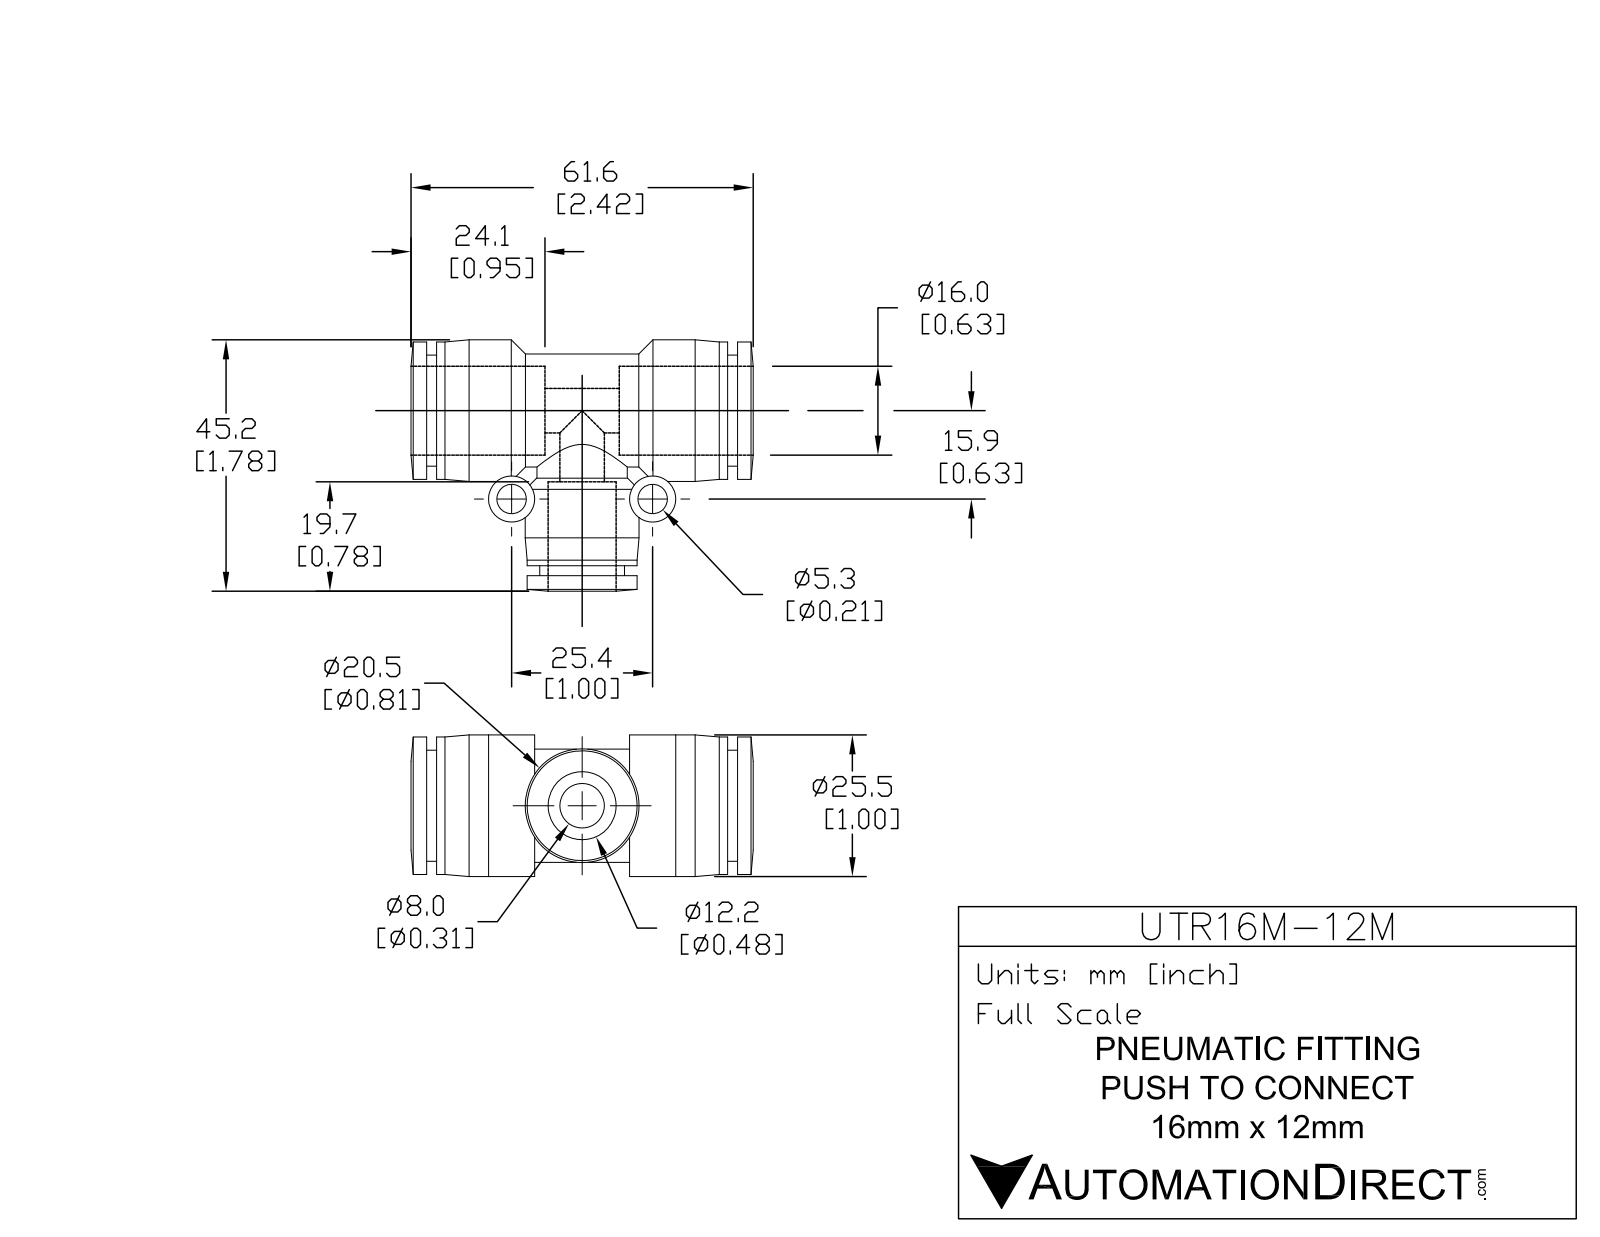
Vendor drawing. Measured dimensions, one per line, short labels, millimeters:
name: UTR16M-12M
written by: SolidWorks 2015 (CONFIG_CONTROL_DESIGN)
unit: mm
bodies: 1 solid, 89 faces (19 planar, 49 cylindrical, 21 other)
size: 61.6 × 45.25 × 25.5
volume: 21 160 mm³; area: 13 504 mm²
holes: 2× ⌀5.3, 2× ⌀8, 1× ⌀12.25, 1× ⌀16
bosses: 2× ⌀8.3, 1× ⌀25.5, 1× ⌀24.74, 1× ⌀20.5, 1× ⌀20.4, 1× ⌀20, 1× ⌀19.8, 1× ⌀16.4
face distances: 1.8, 54.2, 21.3, 34.7, 19.5, 32.9, 56, 52.4, 13.4, 16.9
hole spacings: 25.4
